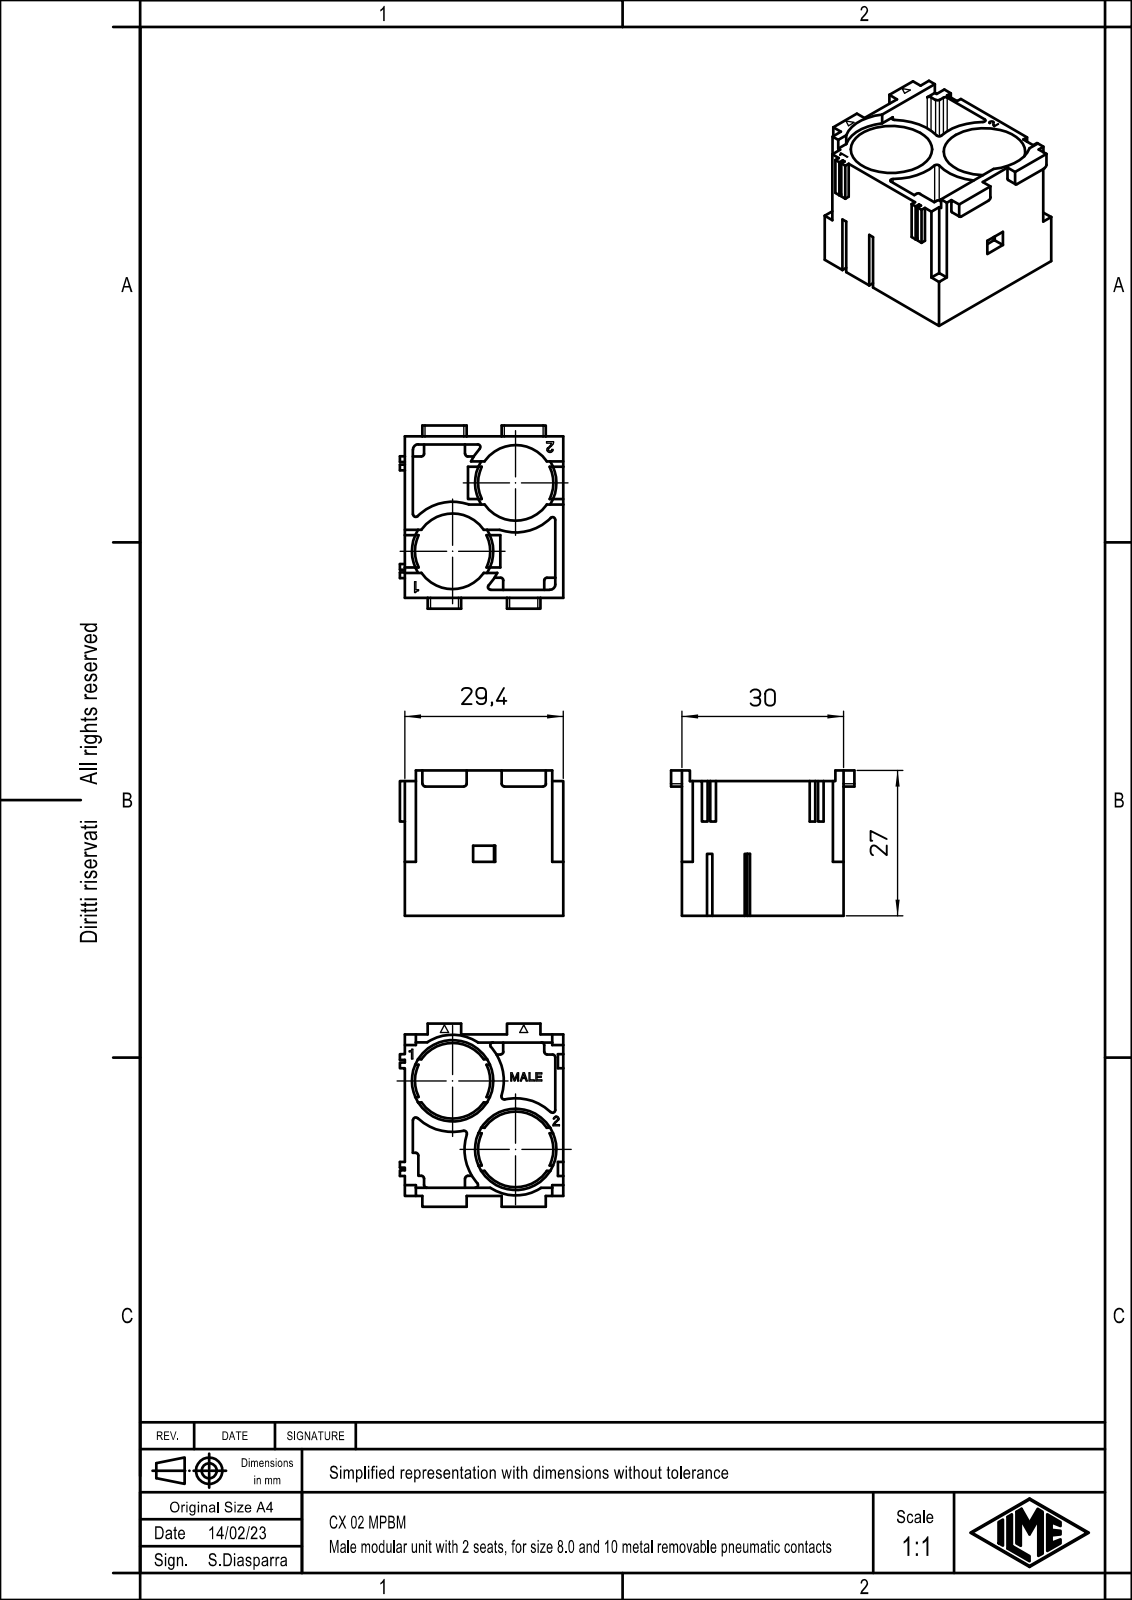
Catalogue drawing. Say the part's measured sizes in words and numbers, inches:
The part is named "CX 02 MPBM". Its 3-D file was written by "Creo Elements/Direct Modeling 20.1B 02-Apr-2019 (C) Parametric Technology GmbH (AUTOMOTIVE_DESIGN)". It is 1 solid with 313 faces: 251 planar, 58 cylindrical and 4 other. Overall it measures 1.339 by 1.193 by 1.063 inches. Its volume is 0.471 cubic inches and its surface area 14.55 square inches. Round holes: 2 of diameter 0.594. Partial cylindrical surfaces (rounded edges, fillets, slot ends): 26 of radius 0.02, 2 of radius 0.039, 2 of radius 0.274, 2 of radius 0.277, 2 of radius 0.337, 2 of radius 0.362, 2 of radius 0.374. The main face-to-face distances are 0.059, 1.181, 1.157, 1.098, 0.079, 0.039, 0.06, 1.121, 0.453, 1.122. The hole center spacings are 0.68.
